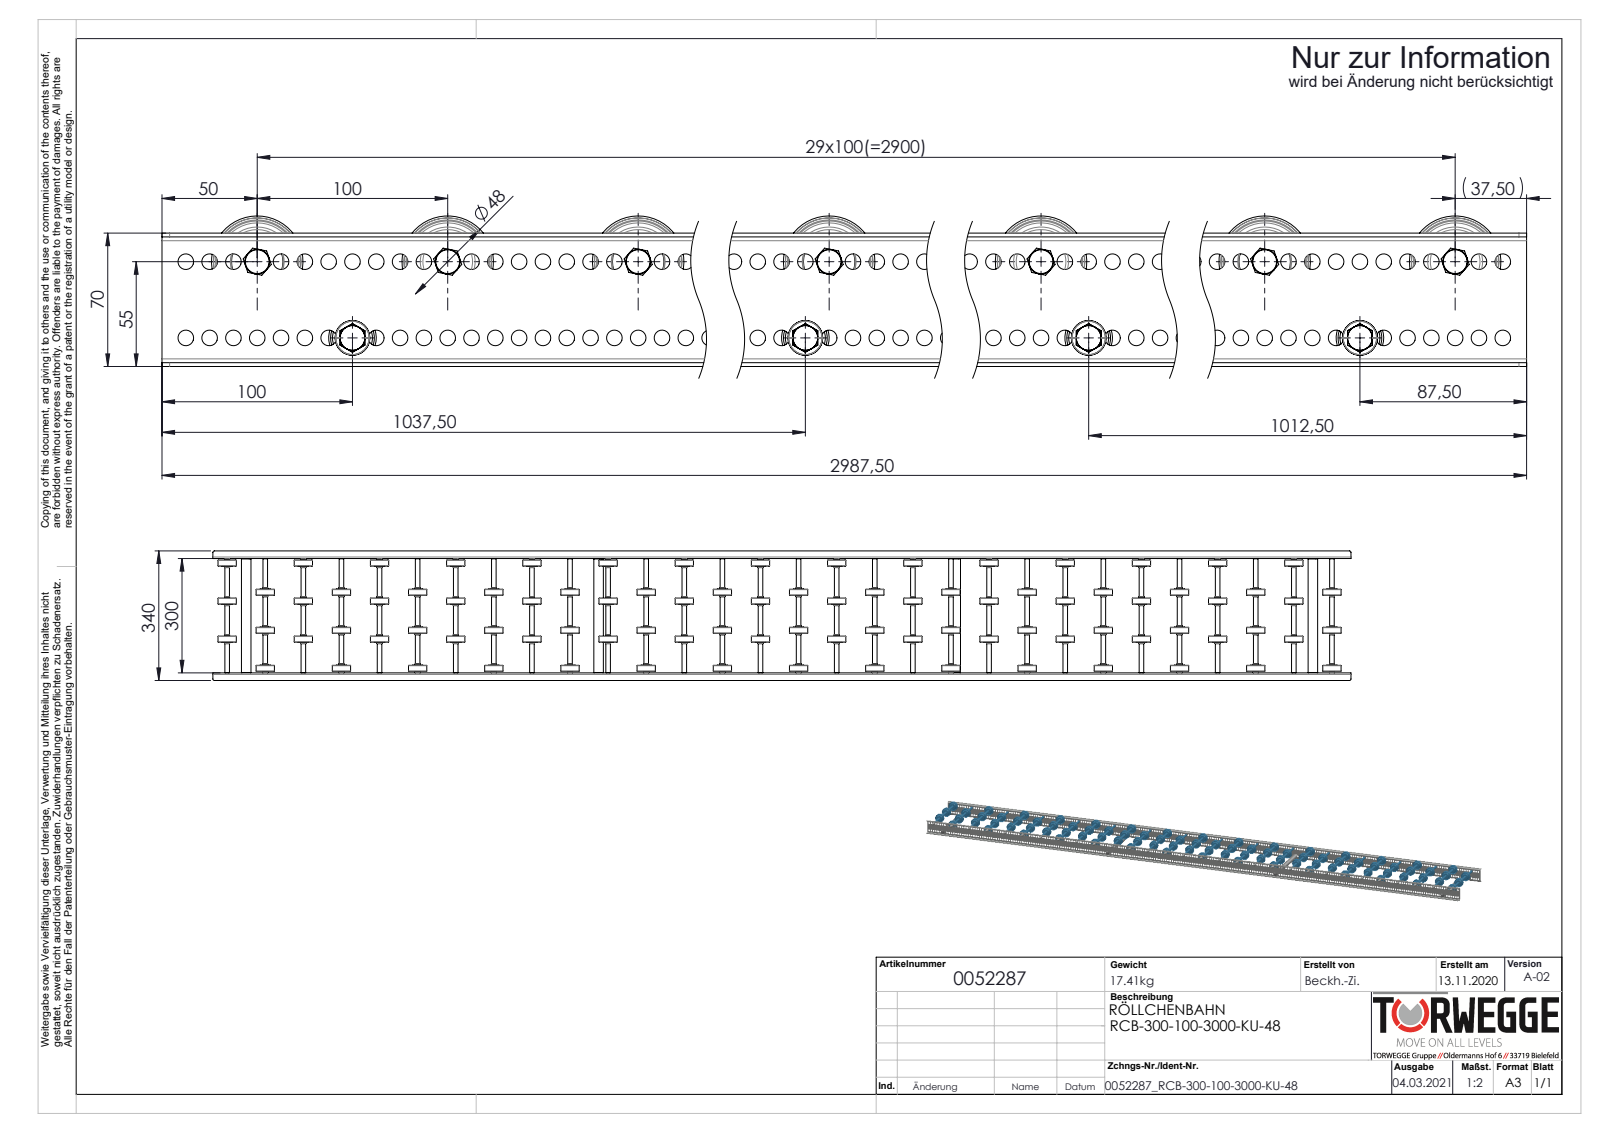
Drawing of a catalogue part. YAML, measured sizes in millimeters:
part_name: "0011532_2300-48-8; S100994_Sperrzahnschraube_M08x16-8.8-A2K; Profil_LRB-20x70x20x2_KFG_S109080_U-PROFIL-20-70-20-2-LRB-L=2987,5; Traversen_KFG_L300 (+5 more)"
step_written_by: "SolidWorks 2020 (AUTOMOTIVE_DESIGN)"
units: millimeters
bodies: {solids: 292, faces: 11082, planar: 1914, cylindrical: 4280, other: 4888}
overall_size: [2987.5, 340, 79]
volume: 3899000
surface_area: 3042000
round_holes:
  - {diameter: 8.2, count: 476}
  - {diameter: 6.65, count: 30}
  - {diameter: 9.65, count: 30}
  - {diameter: 13.7, count: 30}
  - {diameter: 6.8, count: 4}
  - {diameter: 21, count: 4}
round_bosses_or_shafts:
  - {diameter: 8, count: 34}
  - {diameter: 48, count: 30}
  - {diameter: 27, count: 30}
  - {diameter: 12.7, count: 30}
  - {diameter: 12.5, count: 30}
  - {diameter: 12, count: 30}
  - {diameter: 25, count: 4}
partial_cylinders:
  - {radius: 4, count: 8}
  - {radius: 2, count: 4}
face_to_face_distances: [2, 302, 68, 300, 304, 70, 66, 99.8, 16.3, 76.1]
hole_center_spacings: [12.5, 25, 37.5, 50, 62.5, 75, 87.5, 100]
